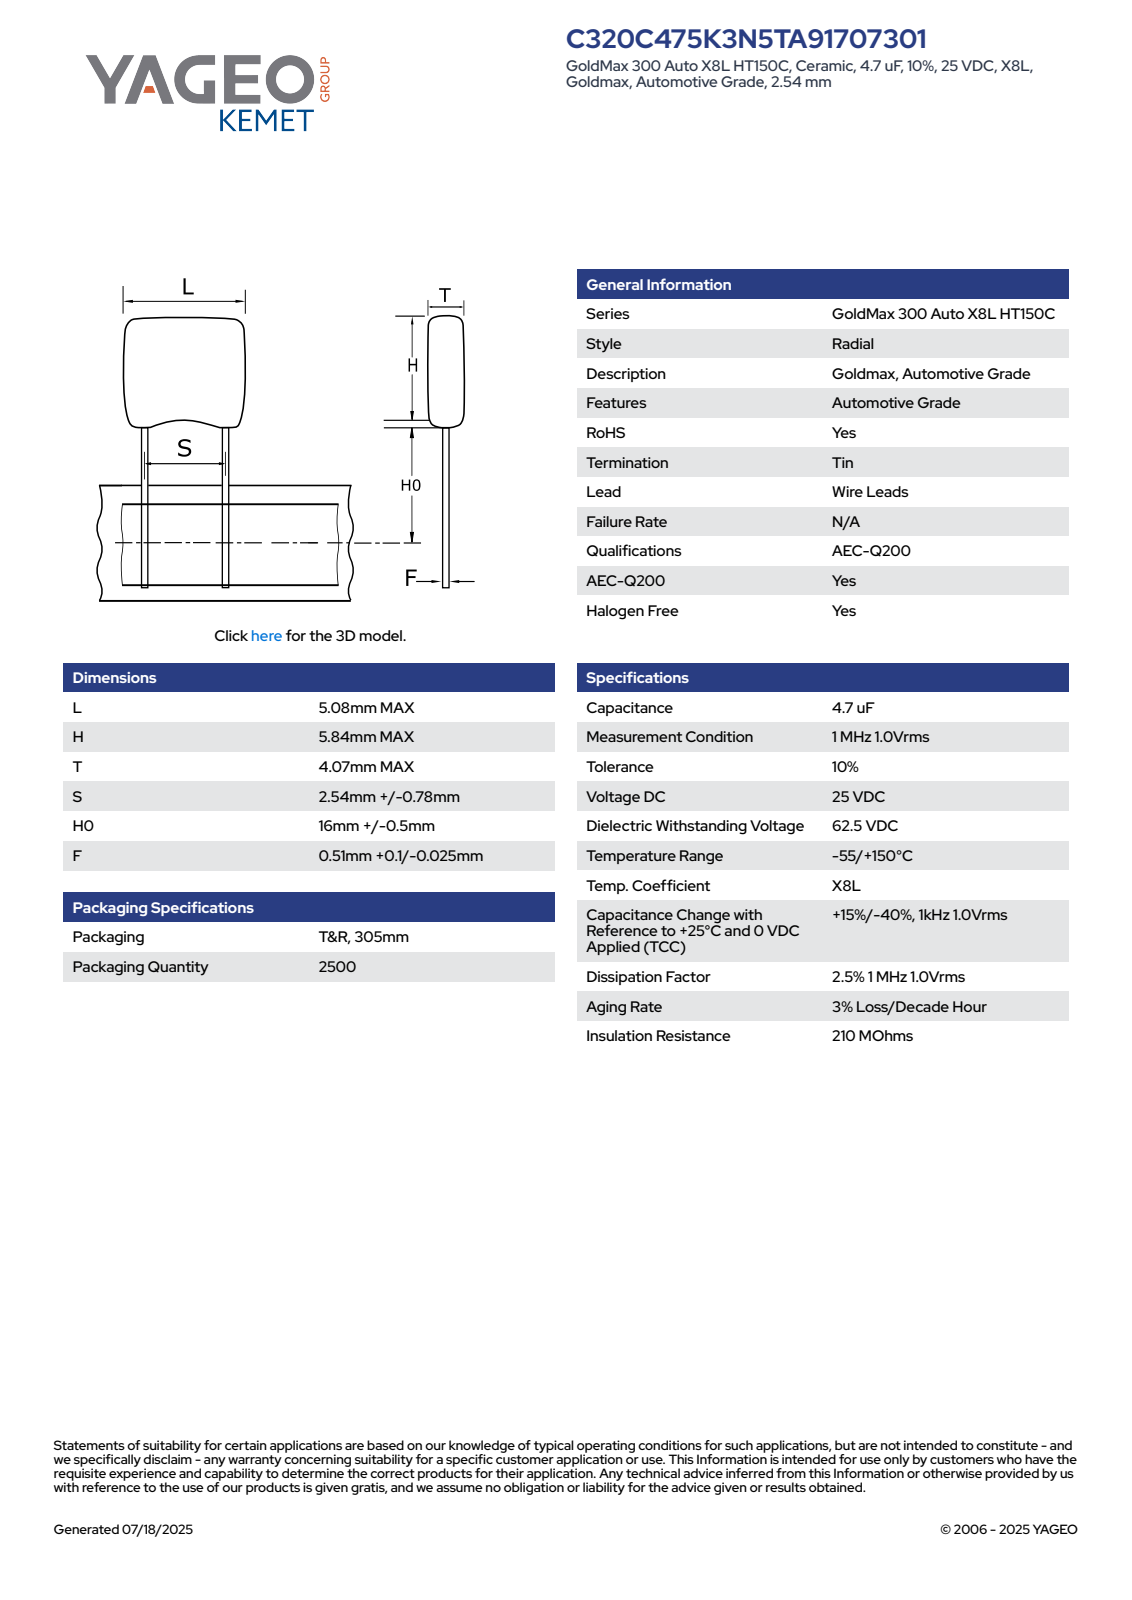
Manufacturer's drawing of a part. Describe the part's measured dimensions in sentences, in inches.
The part is named "CCR_KRCST_5.08X5.84_L5.08H5.84T4.07S2.54H016.5F0.61". Its 3-D file was written by "SolidWorks 2014 (AUTOMOTIVE_DESIGN)". It is 4 solids with 83 faces: 65 planar, 14 cylindrical and 4 other. Overall it measures 0.906 by 0.2 by 0.161 inches. Its volume is 0.008 cubic inches and its surface area 0.321 square inches. Round bosses or shafts: 2 of diameter 0.024. Partial cylindrical surfaces (rounded edges, fillets, slot ends): 10 of radius 0.03. The main face-to-face distances are 0.16, 0.2, 0.256, 0.65, 0.906, 0.161, 0.021, 0.785, 0.135, 0.121.
